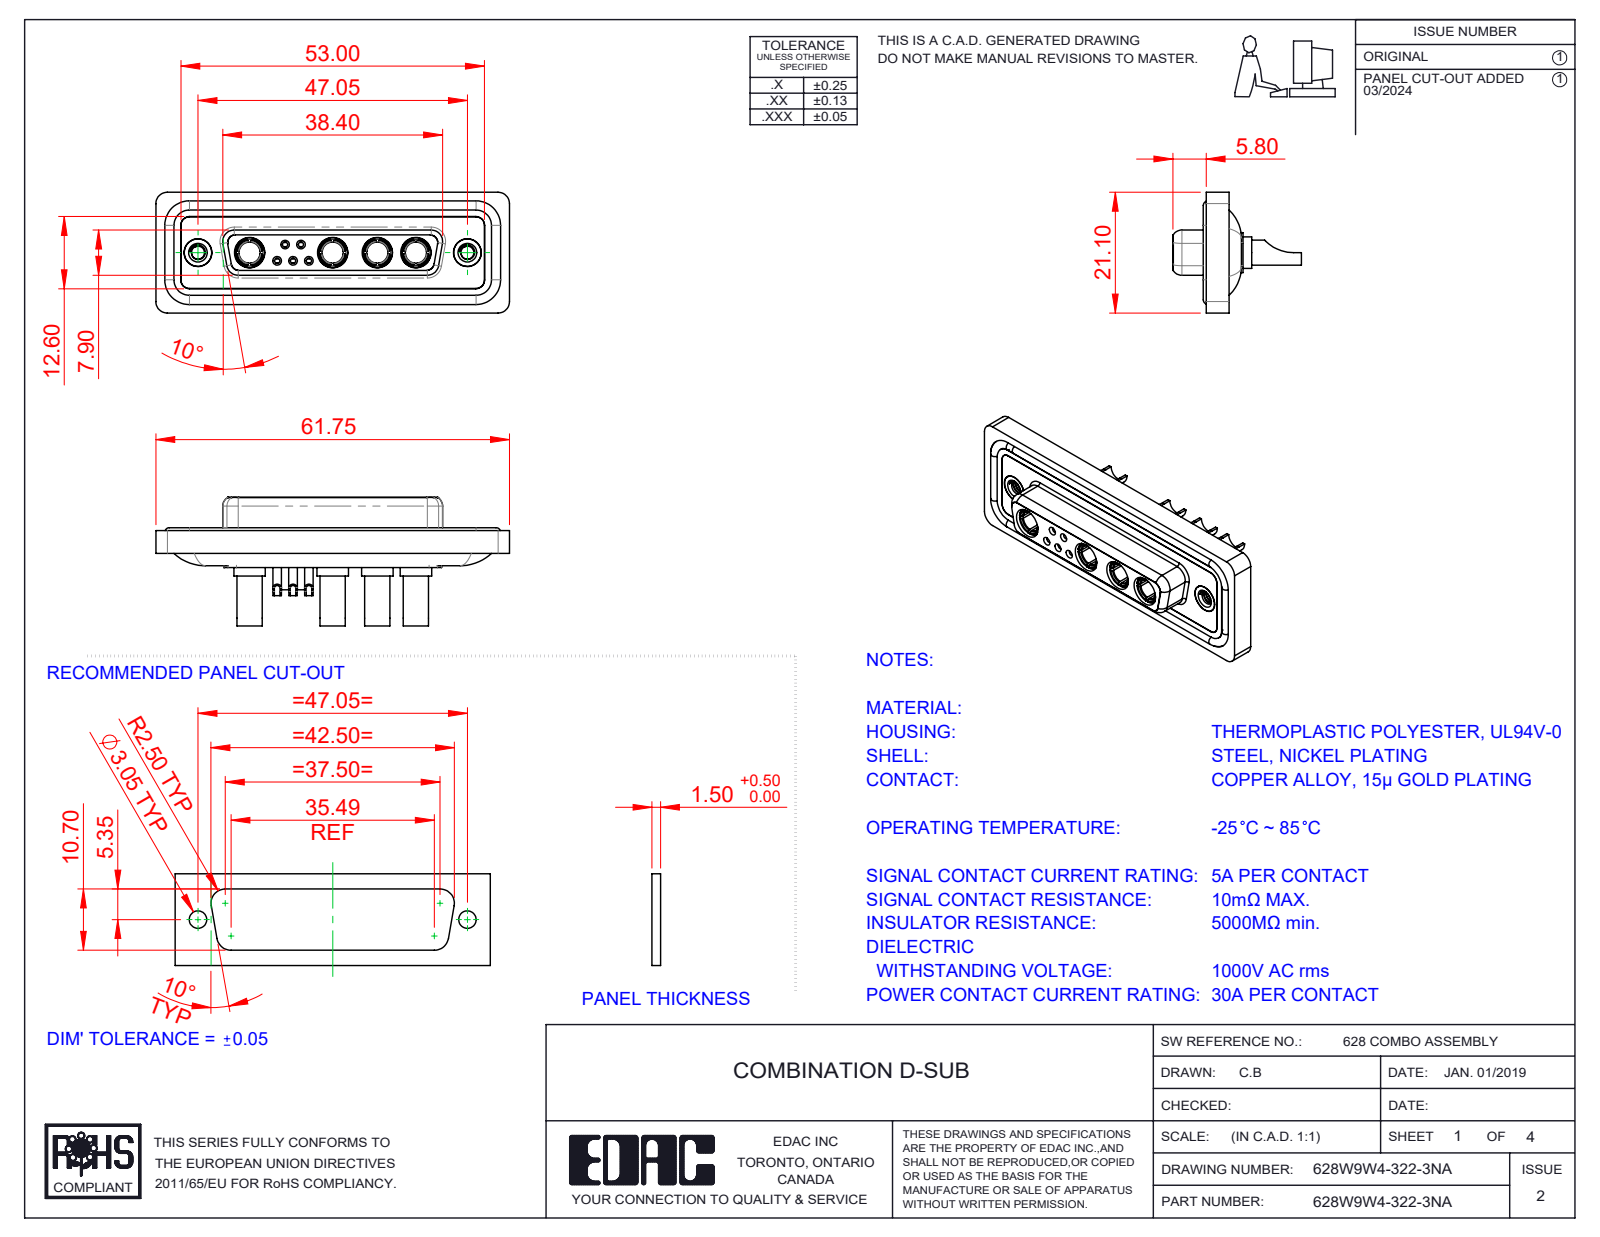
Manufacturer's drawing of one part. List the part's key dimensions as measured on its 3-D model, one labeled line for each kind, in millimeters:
Part name (STEP PRODUCT): 628Combo Contact Row 1_22; 628Combo Shell Rear_25 Contacts; 628W9W4-322-3NA; 628Combo Shell Front_25 Contacts (+5 more)
STEP written by: SolidWorks 2023 (CONFIG_CONTROL_DESIGN)
Units: millimetres
Bodies: 20 solids, 979 faces (318 planar, 399 cylindrical, 262 other)
Overall size (bounding box): 61.75 × 22.45 × 21.1
Volume: 8 332 mm³ · Surface area: 14 045 mm²
Round holes (diameter × count): ⌀4.85 ×6, ⌀0.9 ×5, ⌀1 ×5, ⌀1.1 ×5, ⌀1.5 ×5, ⌀2 ×5, ⌀3.5 ×4, ⌀3.7 ×4, ⌀5.3 ×4, ⌀1.6 ×3, ⌀1.7 ×2, ⌀2.26 ×2
Round bosses / shafts (diameter × count): ⌀1.6 ×6, ⌀2.2 ×5, ⌀5.5 ×4, ⌀5.2 ×4, ⌀4.96 ×4, ⌀4.75 ×4, ⌀4.4 ×4, ⌀3.75 ×4
Partial cylindrical surfaces — rounded edges, fillets, slot ends (radius × count): R1.5 ×22, R2 ×18, R1.35 ×8, R1.6 ×8, R1 ×6, R0.25 ×4, R0.5 ×4, R0.6 ×4
Main face-to-face distances: 0.4, 1.8, 7.45, 5.65, 0.5, 7.05, 6.6, 1.6, 1.1, 2.9
Hole centre spacings: 3.16, 2.77, 5.03, 2.76, 4.4, 5.02, 5.54, 5.73
